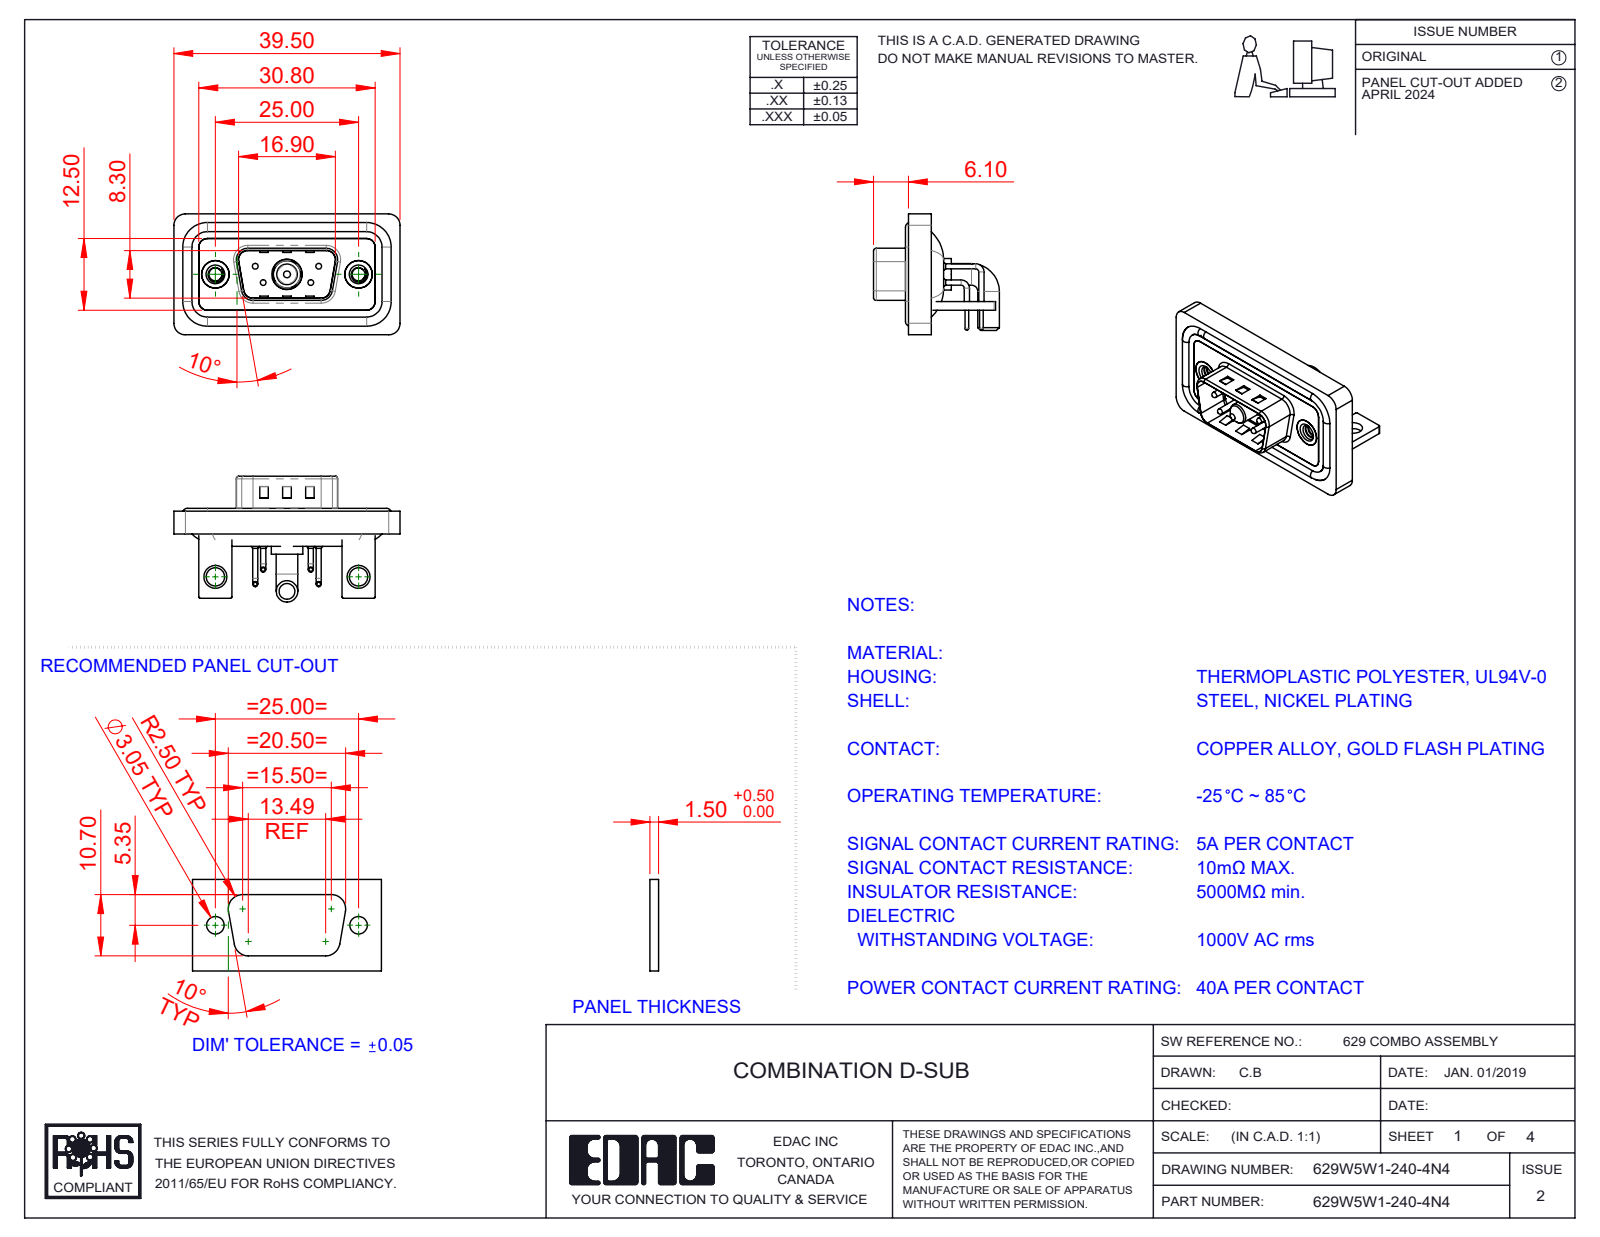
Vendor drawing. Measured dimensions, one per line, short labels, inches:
name: 629Combo Stabilizer Bracket; 629Combo Shell Front_09 Contacts; 629Combo Threaded Rivet_3; 629Combo Shell Rear_09 Contacts (+6 more)
written by: SolidWorks 2023 (CONFIG_CONTROL_DESIGN)
unit: in
bodies: 15 solids, 934 faces (431 planar, 363 cylindrical, 140 other)
size: 1.555 × 0.865 × 0.831
volume: 0.295 in³; area: 12.08 in²
holes: 4× ⌀0.03, 4× ⌀0.063, 4× ⌀0.079, 2× ⌀0.089, 2× ⌀0.126, 2× ⌀0.157, 2× ⌀0.189, 2× ⌀0.197, 1× ⌀0.191, 1× ⌀0.209
bosses: 8× ⌀0.035, 4× ⌀0.063, 4× ⌀0.059, 4× ⌀0.039, 4× ⌀0.026, 2× ⌀0.193, 2× ⌀0.148, 1× ⌀0.217
rounds: 19× R0.079, 18× R0.059, 16× R0.01, 9× R0.02, 8× R0.063, 4× R0.024, 4× R0.026, 4× R0.035
face distances: 0.016, 0.059, 0.031, 0.114, 0.043, 0.083, 0.047, 0.063, 0.098, 0.146
hole spacings: 0.124, 0.225, 0.28, 0.492, 0.713, 0.984, 0.173, 0.173
